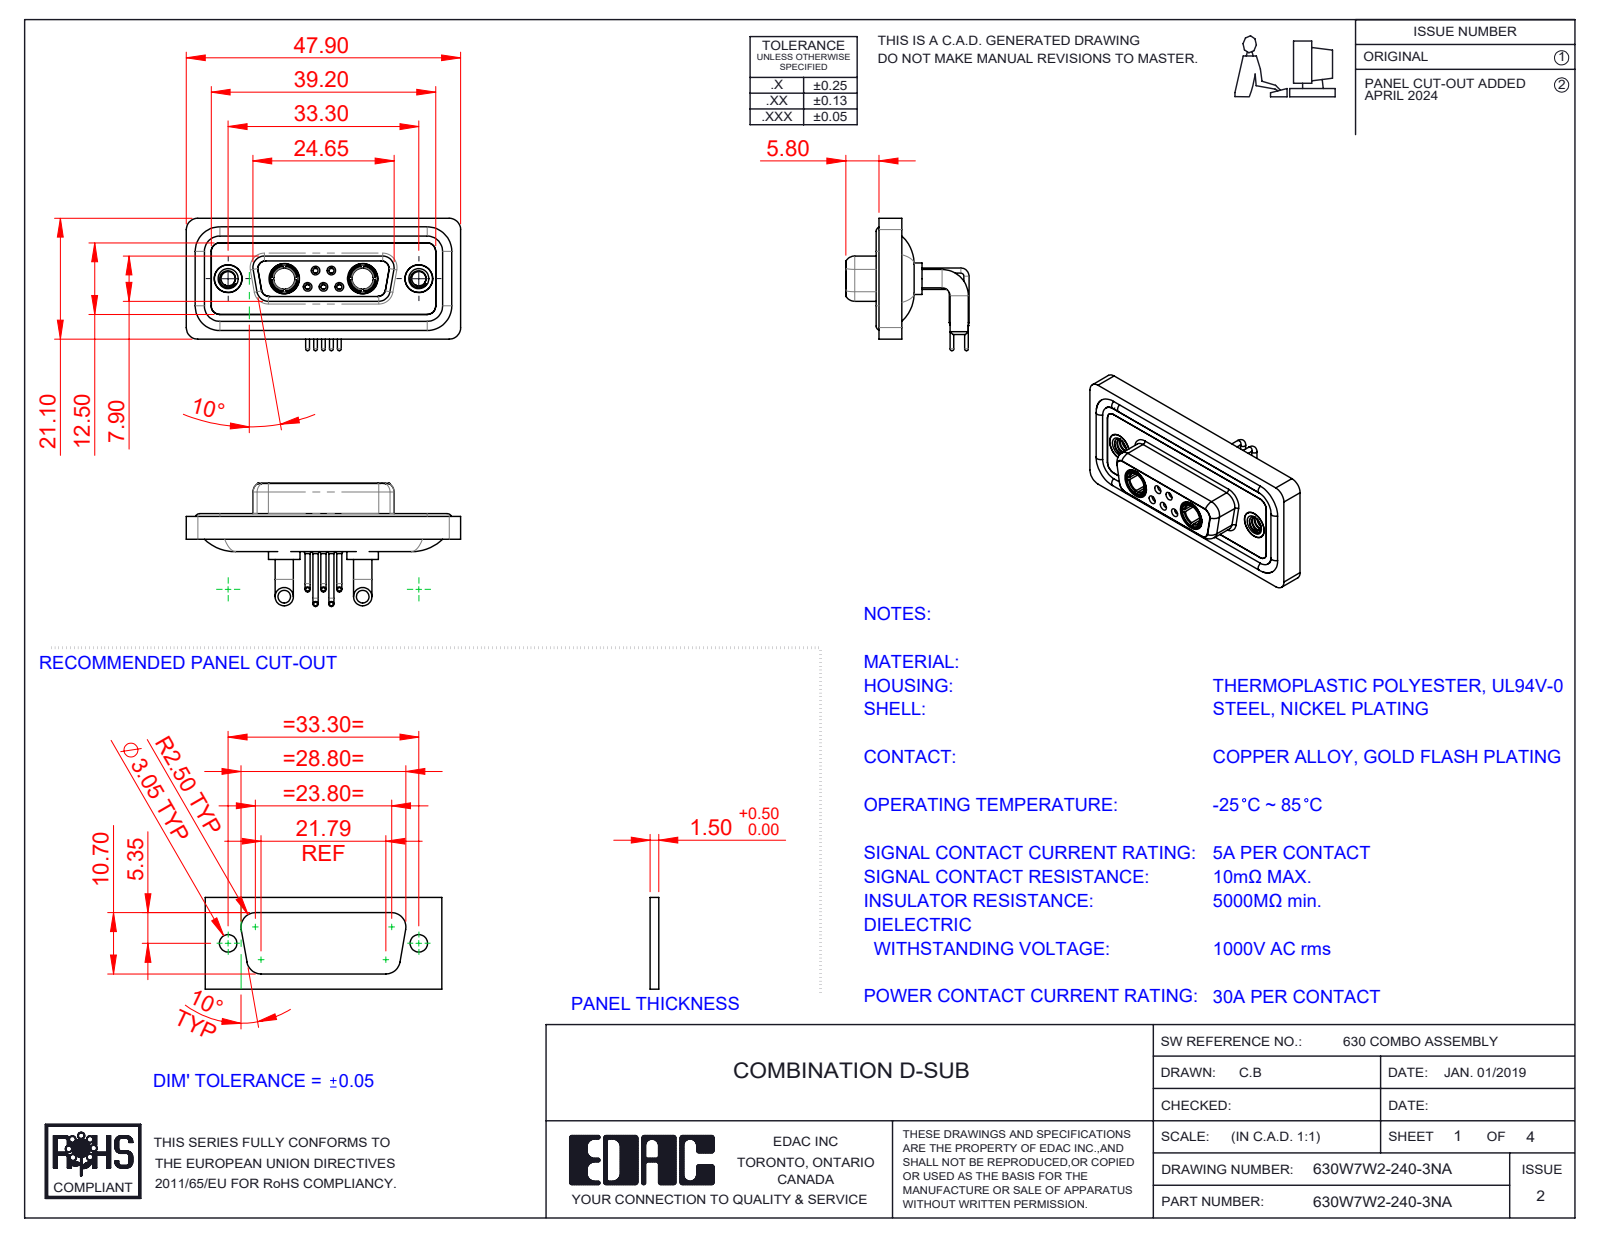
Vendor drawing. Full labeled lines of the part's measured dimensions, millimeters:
Part name (STEP PRODUCT): 630Combo Threaded Rivet_A; 630W7W2-140-3NA; 630Combo Contact Row 1_50 Contacts; 630Combo Shell Front_15 Contacts (+5 more)
STEP written by: SolidWorks 2023 (CONFIG_CONTROL_DESIGN)
Units: millimetres
Bodies: 16 solids, 801 faces (238 planar, 351 cylindrical, 212 other)
Overall size (bounding box): 47.9 × 23.12 × 21.53
Volume: 6 245 mm³ · Surface area: 10 245 mm²
Round holes (diameter × count): ⌀0.9 ×5, ⌀1.1 ×5, ⌀1.5 ×5, ⌀2 ×5, ⌀4.85 ×4, ⌀1.6 ×3, ⌀1.7 ×2, ⌀2.5 ×2, ⌀3.7 ×2, ⌀4 ×2, ⌀4.05 ×2, ⌀5 ×2
Round bosses / shafts (diameter × count): ⌀1.6 ×6, ⌀0.9 ×5, ⌀0.65 ×5, ⌀3.2 ×4, ⌀5.5 ×2, ⌀5.2 ×2, ⌀4.96 ×2, ⌀4.95 ×2
Partial cylindrical surfaces — rounded edges, fillets, slot ends (radius × count): R2 ×20, R1.5 ×18, R1.35 ×12, R1.6 ×8, R0.25 ×4, R0.5 ×4, R0.6 ×4, R0.65 ×4
Main face-to-face distances: 0.4, 1.8, 1.1, 1.6, 2.9, 2.5, 3.1, 3.7, 4.1, 1.5
Hole centre spacings: 3.16, 2.77, 9.8, 23.5, 4.31, 4.33, 5.03, 5.04
